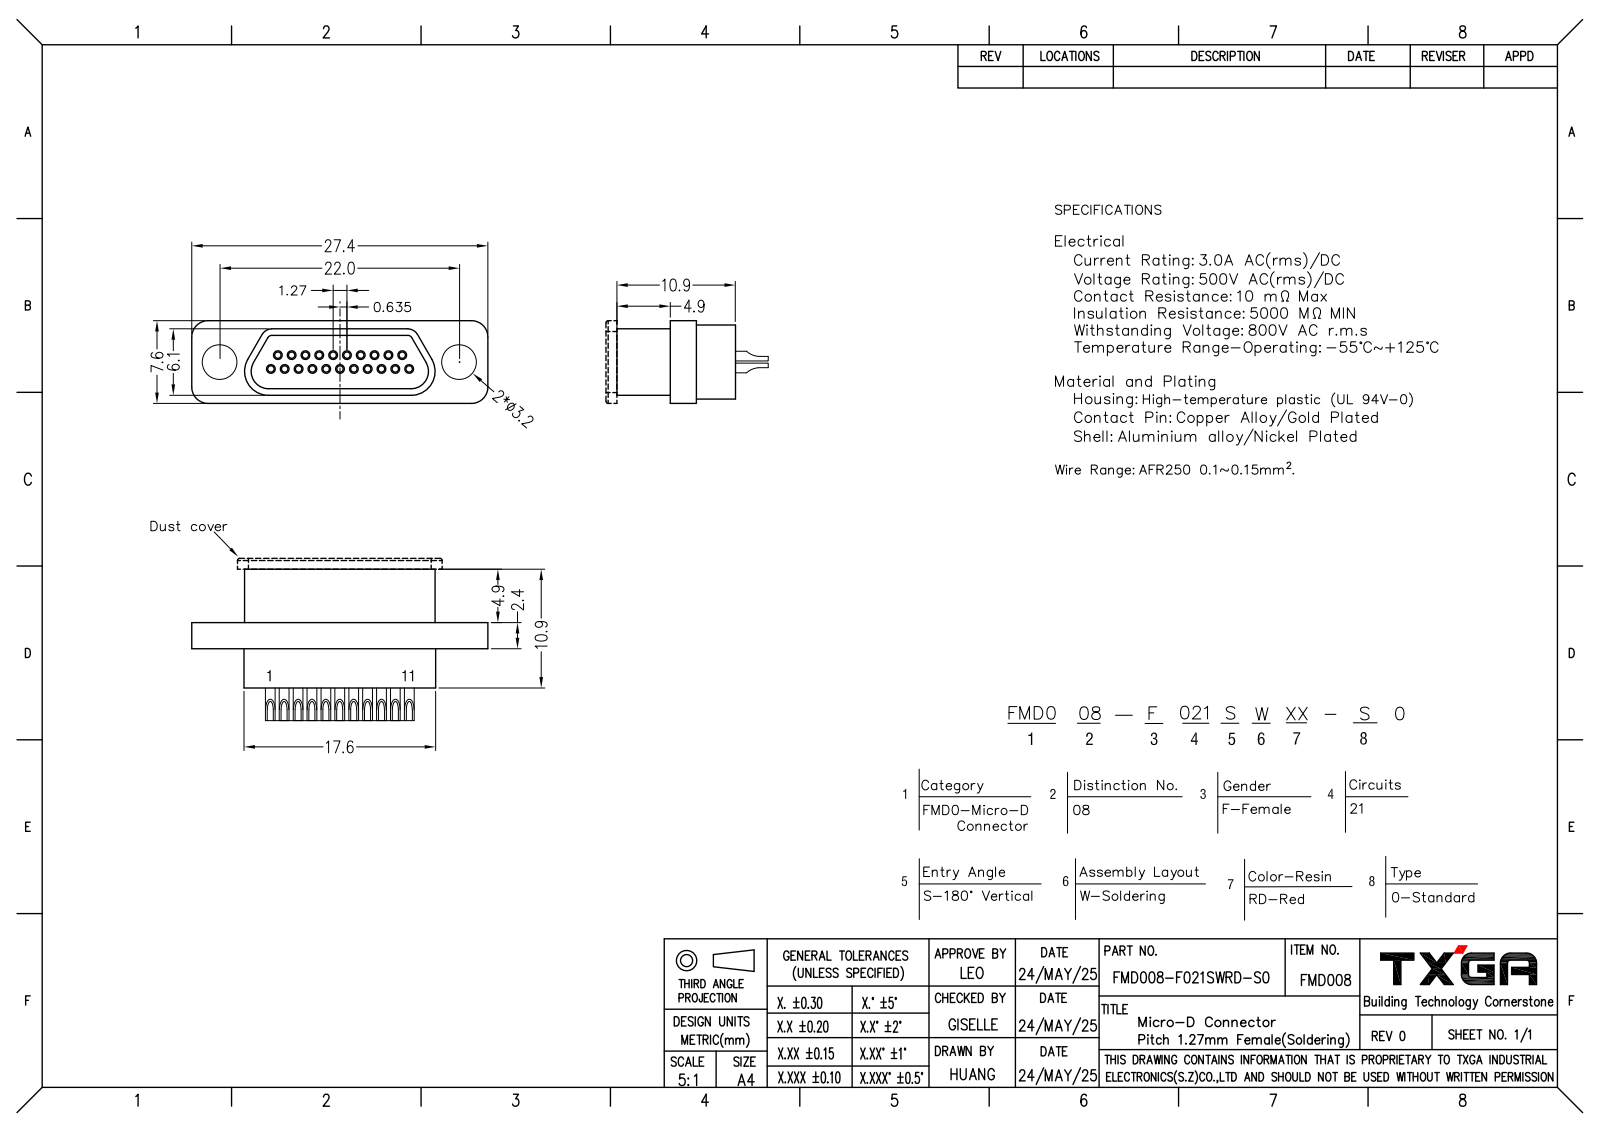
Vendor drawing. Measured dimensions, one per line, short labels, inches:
name: FMD008-F021SWRD-S0
written by: SolidWorks 2021 (CONFIG_CONTROL_DESIGN)
unit: in
bodies: 1 solid, 1115 faces (610 planar, 213 cylindrical, 292 other)
size: 1.079 × 0.547 × 0.299
volume: 0.064 in³; area: 2.612 in²
holes: 21× ⌀0.02, 21× ⌀0.022, 2× ⌀0.126
bosses: 21× ⌀0.035
rounds: 4× R0.059, 4× R0.063, 4× R0.071, 4× R0.087, 2× R0.039
face distances: 0.024, 0.236, 0.246, 0.03, 0.27, 0.053, 0.217, 0.037, 0.016, 0.283
hole spacings: 0.05, 0.087, 0.1, 0.132, 0.15, 0.2, 0.25, 0.3
